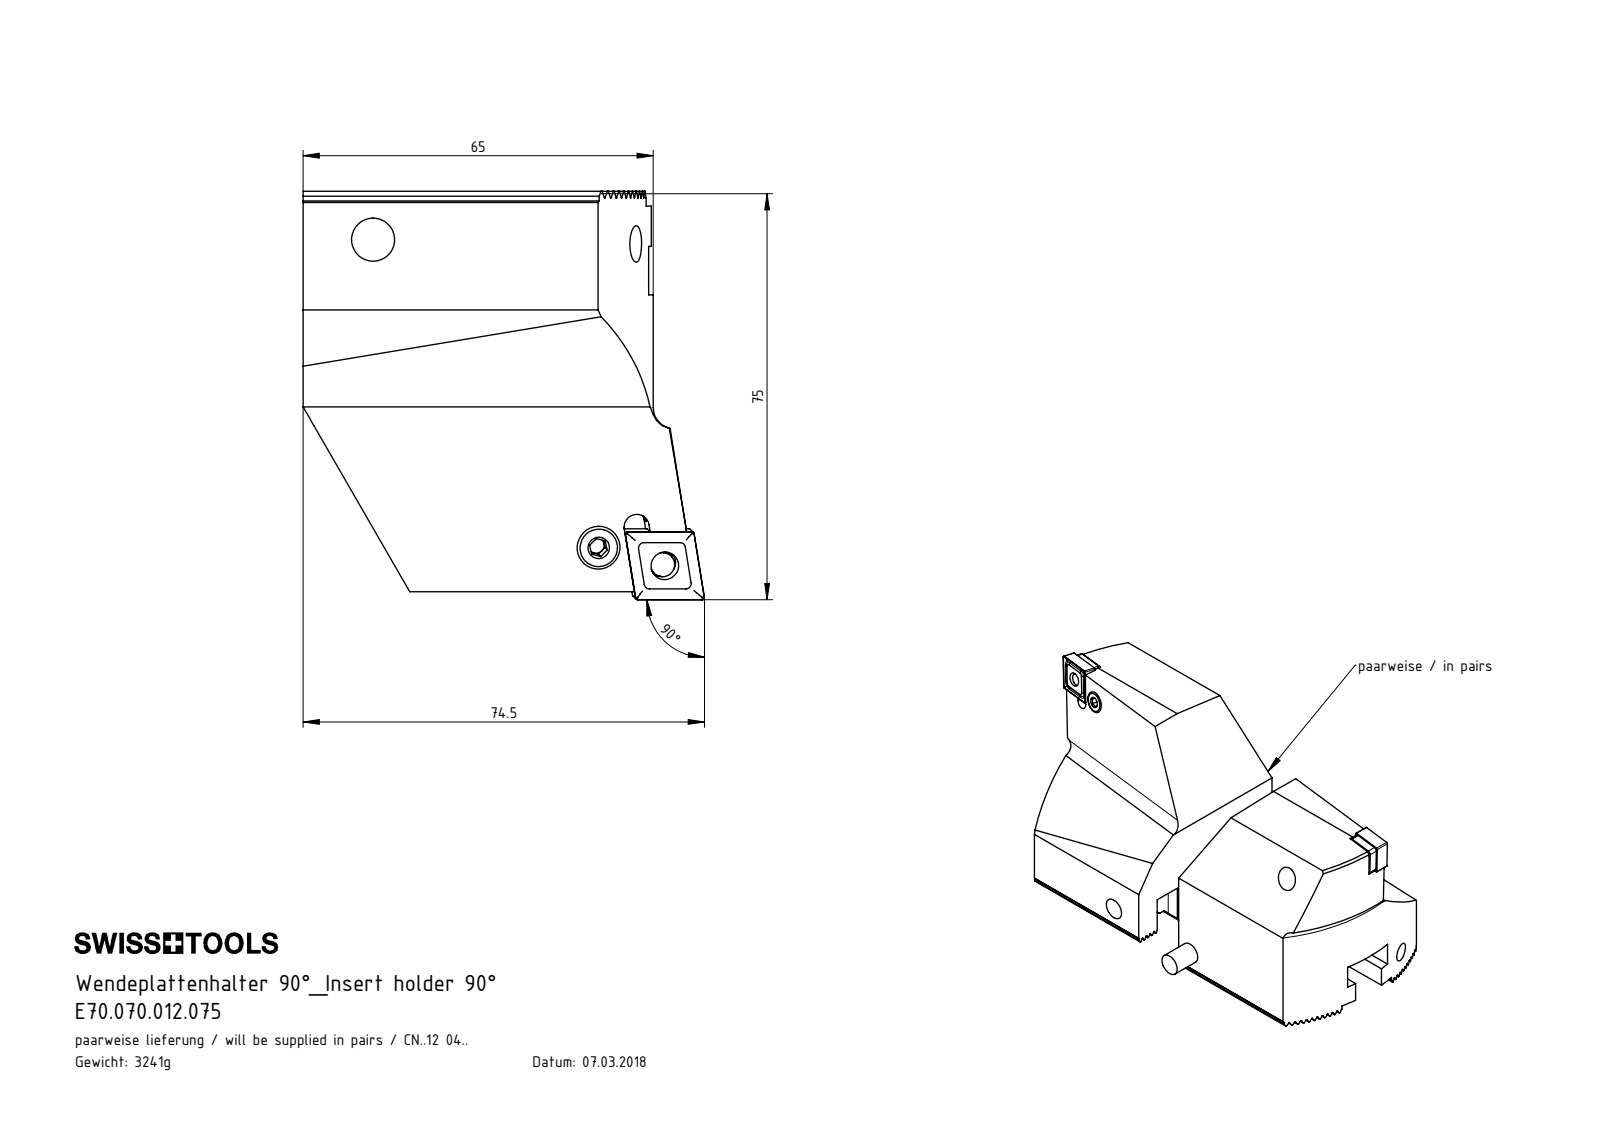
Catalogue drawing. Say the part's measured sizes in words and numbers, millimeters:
The part is named "ISO 8734 - 8 x 20 m6; E70.070.012.075; VK1-WCD.101.075_A; WCD-ER4.101.017_A (+6 more)". Its 3-D file was written by "SolidWorks 2017 (CONFIG_CONTROL_DESIGN)". It is 16 solids with 1263 faces: 759 planar, 164 cylindrical and 340 other. Overall it measures 205.01 by 94 by 75.79 millimeters. Its volume is 413 723 cubic millimeters and its surface area 67 086 square millimeters. Round holes: 4 of diameter 8, 2 of diameter 5.16, 2 of diameter 6.4, 2 of diameter 6.8, 2 of diameter 7, 2 of diameter 8.4. Round bosses or shafts: 3 of diameter 8, 2 of diameter 7.9, 2 of diameter 6.4, 2 of diameter 4.5, 2 of diameter 3.55, 1 of diameter 5.5. Partial cylindrical surfaces (rounded edges, fillets, slot ends): 22 of radius 0.14, 8 of radius 0.4, 8 of radius 1, 6 of radius 2.5, 2 of radius 2.1, 2 of radius 2.2, 2 of radius 2.35, 2 of radius 2.8. The main face-to-face distances are 1.73, 8.66, 3.46, 70, 6.93, 5.2, 43.3, 24.5, 45.5, 10.39. The hole center spacings are 7, 12.8, 12.86, 75, 40, 68, 82.
